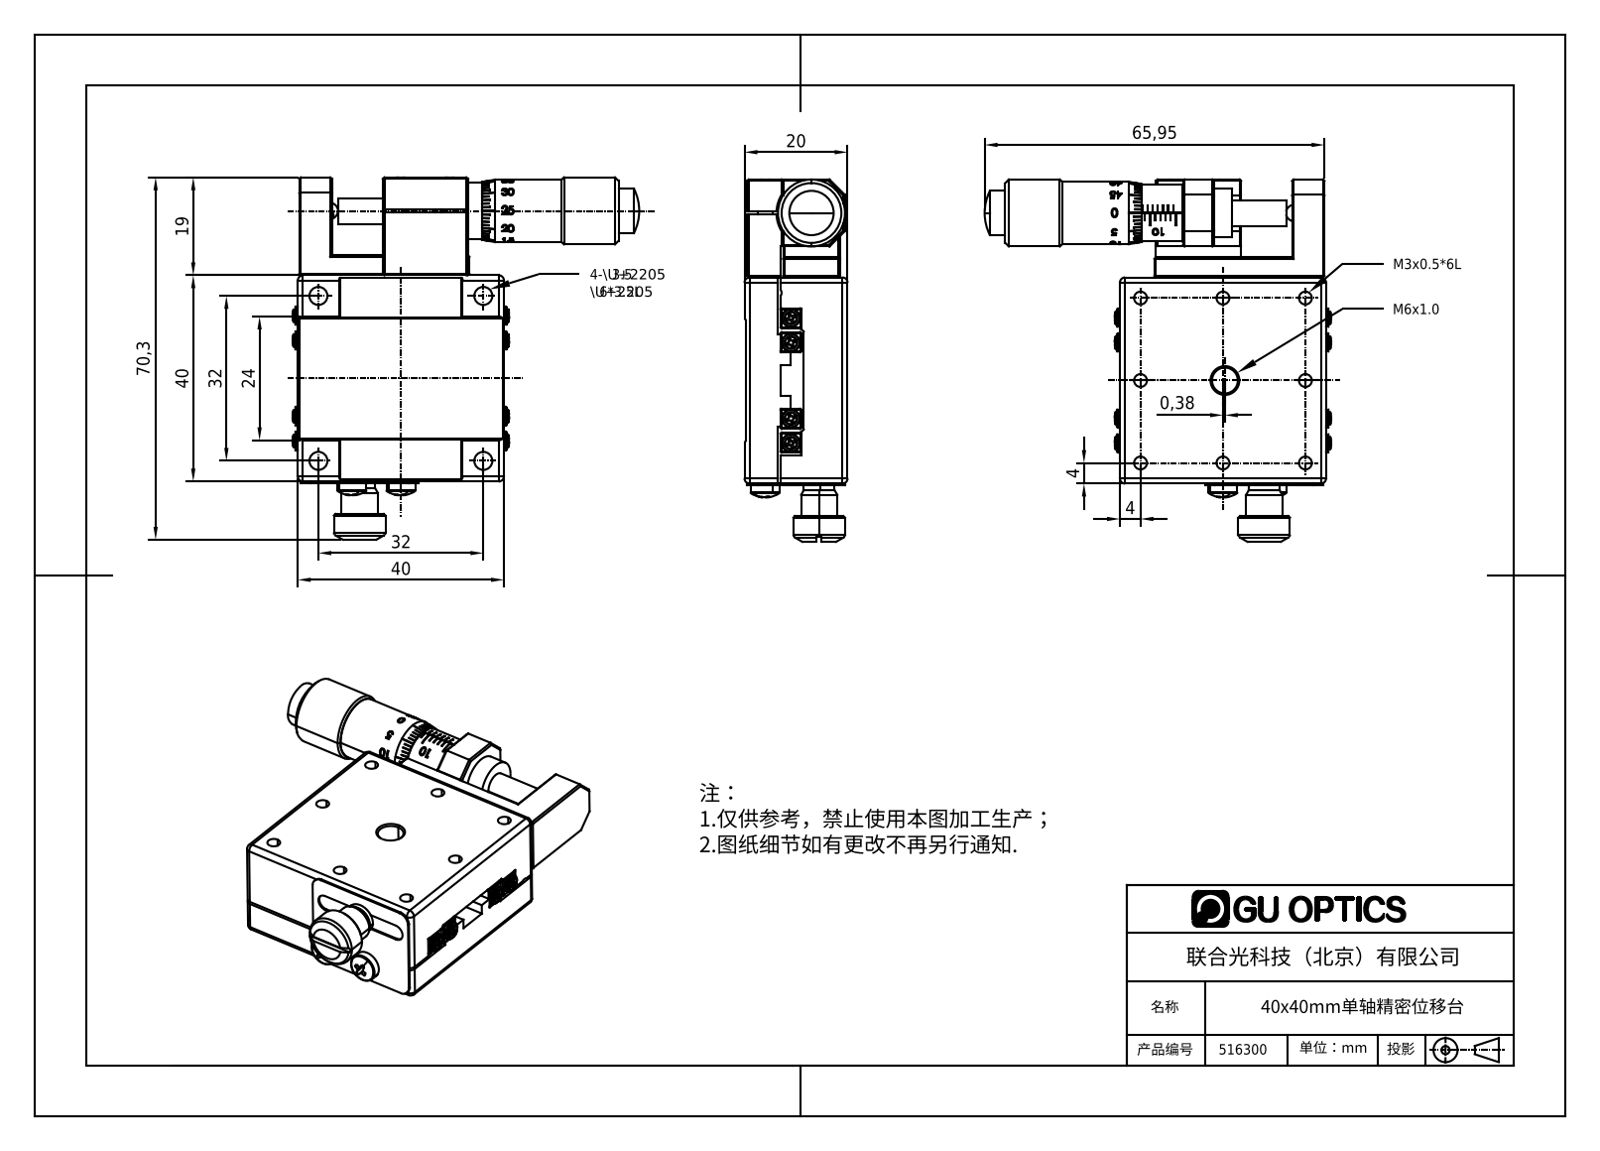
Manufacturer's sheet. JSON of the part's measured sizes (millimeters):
{"part_name": "MX40-AS", "step_written_by": "SolidWorks 2020 (CONFIG_CONTROL_DESIGN)", "units": "millimeters", "bodies": {"solids": 9, "faces": 1429, "planar": 771, "cylindrical": 235, "other": 423}, "overall_size": [70.3, 67.23, 20], "volume_mm3": 38943, "surface_area_mm2": 18703, "round_holes": [[2.5, 8], [3.5, 4], [3.4, 2], [5, 2], [6, 2], [2.05, 1], [2.9, 1], [3, 1], [9.5, 1], [11, 1], [13, 1]], "round_bosses_or_shafts": [[5.5, 4], [3.5, 4], [3, 4], [2.5, 4], [5.6, 2], [1.6, 2], [12.1, 1], [10, 1]], "partial_cylinders_radius": [[1, 13], [1.75, 6], [2, 4], [3, 3], [1.65, 2], [5.48, 1], [5.49, 1], [6.04, 1]], "face_to_face_distances": [0.5, 8.5, 4.5, 13, 40, 11, 6.7, 19.7, 13.5, 6.2], "hole_center_spacings": [16, 35.78, 32, 22.63, 4.76, 22.36, 22.9, 45.25]}
